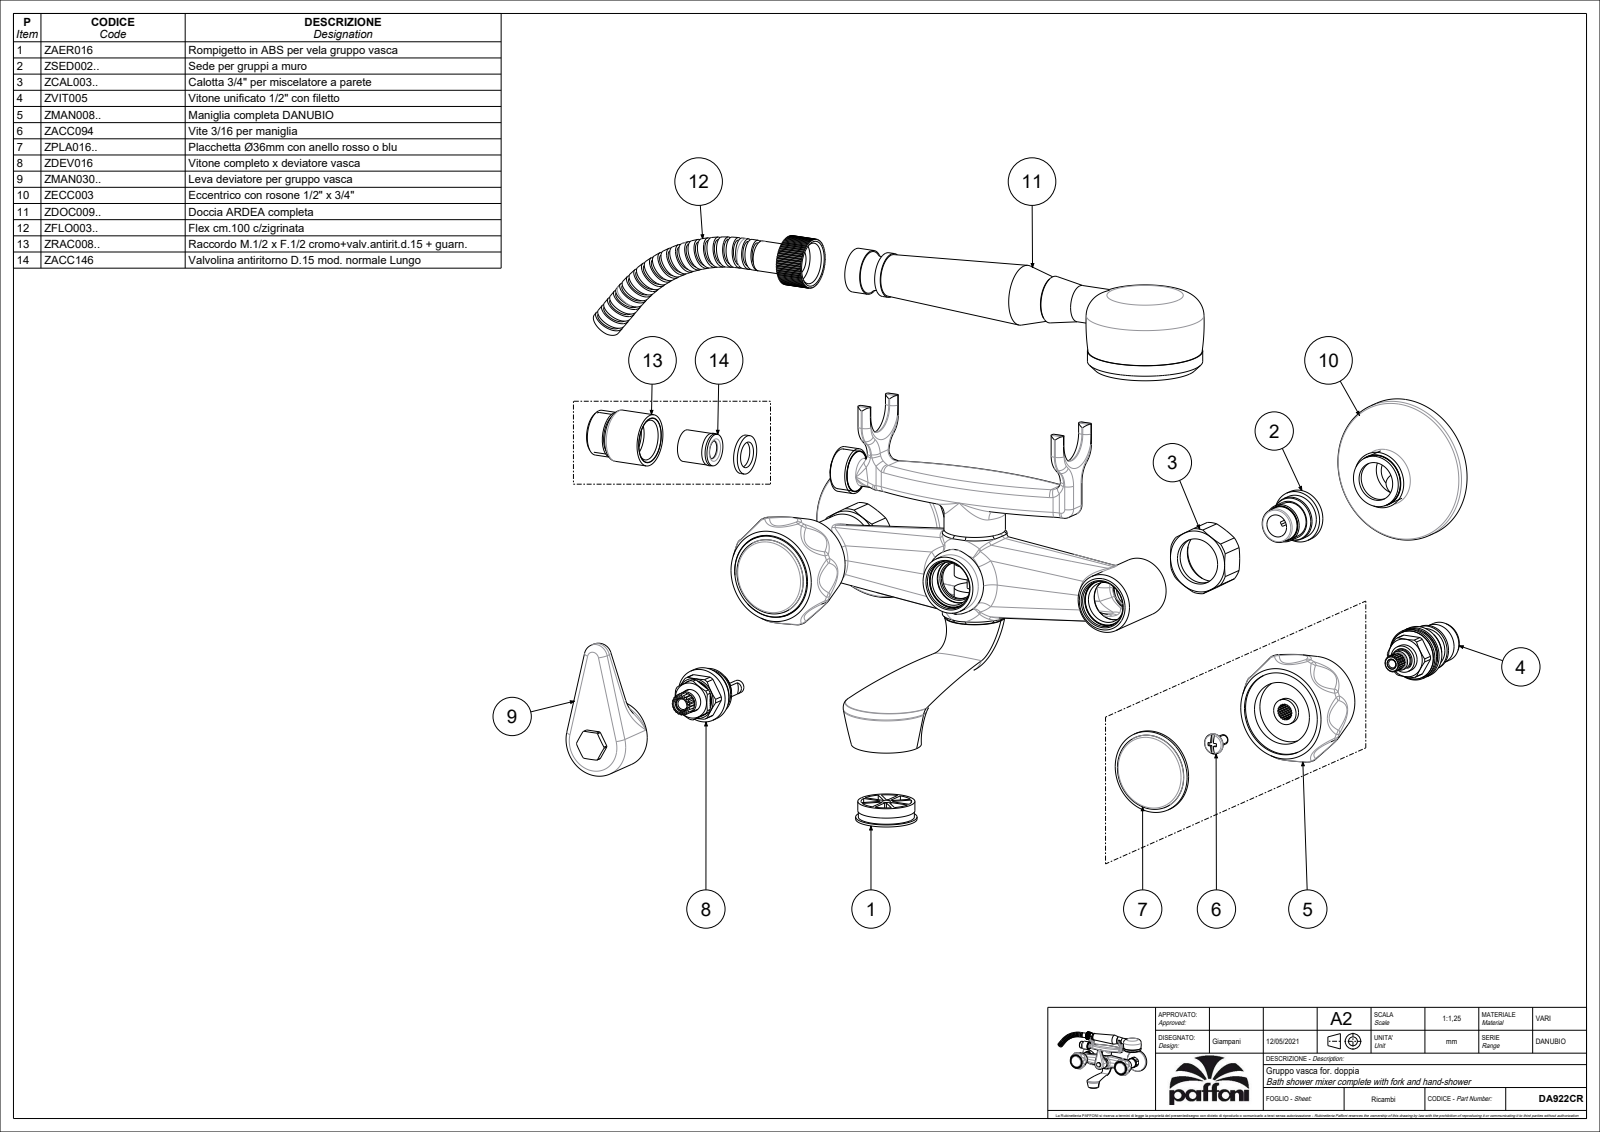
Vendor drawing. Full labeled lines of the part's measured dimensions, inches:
Part name (STEP PRODUCT): DA922CR
STEP written by: CREO PARAMETRIC BY PTC INC, 2020044 (CONFIG_CONTROL_DESIGN)
Units: inches
Bodies: 4 solids, 1799 faces (647 planar, 596 cylindrical, 556 other)
Overall size (bounding box): 11.485 × 6.102 × 5.906
Volume: 28.48 in³ · Surface area: 240.9 in²
Round holes (diameter × count): ⌀0.039 ×108, ⌀0.413 ×3, ⌀0.984 ×3, ⌀0.709 ×2, ⌀0.846 ×2, ⌀0.949 ×2, ⌀1.051 ×2, ⌀1.409 ×2, ⌀1.535 ×2, ⌀2.575 ×2, ⌀0.157 ×1, ⌀0.276 ×1
Round bosses / shafts (diameter × count): ⌀0.945 ×3, ⌀0.807 ×3, ⌀2.598 ×2, ⌀1.516 ×2, ⌀1.201 ×2, ⌀1.122 ×2, ⌀1.083 ×2, ⌀1.008 ×2
Partial cylindrical surfaces — rounded edges, fillets, slot ends (radius × count): R0.039 ×28, R0.118 ×25, R0.839 ×16, R0.394 ×8, R0.197 ×6, R0.059 ×4, R0.236 ×3, R0.61 ×3
Main face-to-face distances: 0.039, 0.472, 0.512, 1.142, 0.374, 0.26, 0.059, 0.295, 0.11, 3.11
Hole centre spacings: 0.323, 0.082, 0.856, 0.164, 0.888, 0.668, 0.774, 0.818
